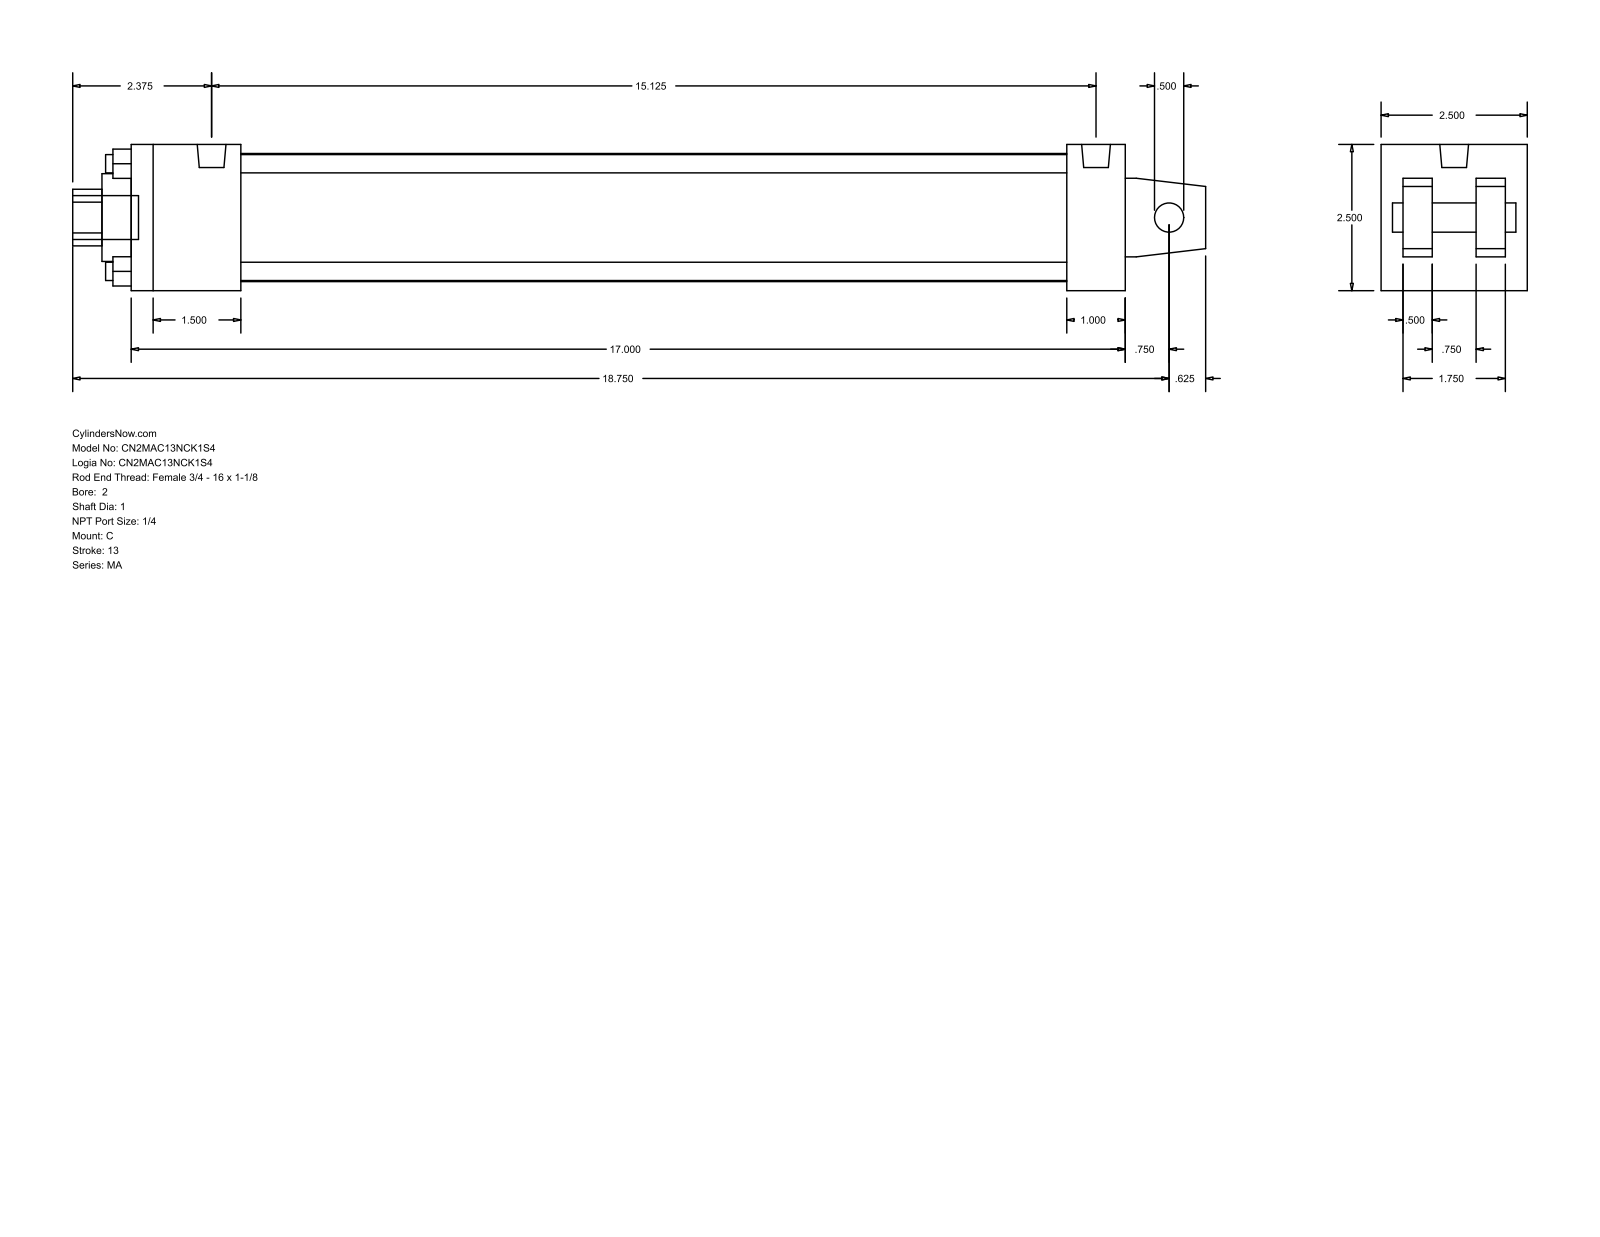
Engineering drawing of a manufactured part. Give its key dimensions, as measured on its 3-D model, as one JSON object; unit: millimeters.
{"part_name": "MA_C__0200_1", "step_written_by": "GSSL Pune (CONFIG_CONTROL_DESIGN)", "units": "millimeters", "bodies": {"solids": 0, "faces": 103, "planar": 76, "cylindrical": 27, "other": 0}, "overall_size": [492.12, 63.5, 63.5], "round_holes": [[7.94, 4], [12.7, 1], [25.4, 1], [38.1, 1], [55.63, 1]], "round_bosses_or_shafts": [[7.94, 4], [12.49, 2], [19.05, 1]], "partial_cylinders_radius": [[12.29, 1]], "face_to_face_distances": [63.5, 12.7, 431.8, 22.22, 41.28, 9.52, 53.98, 31.76, 47.63, 25.4], "hole_center_spacings": [33.05, 46.74, 66.1]}
